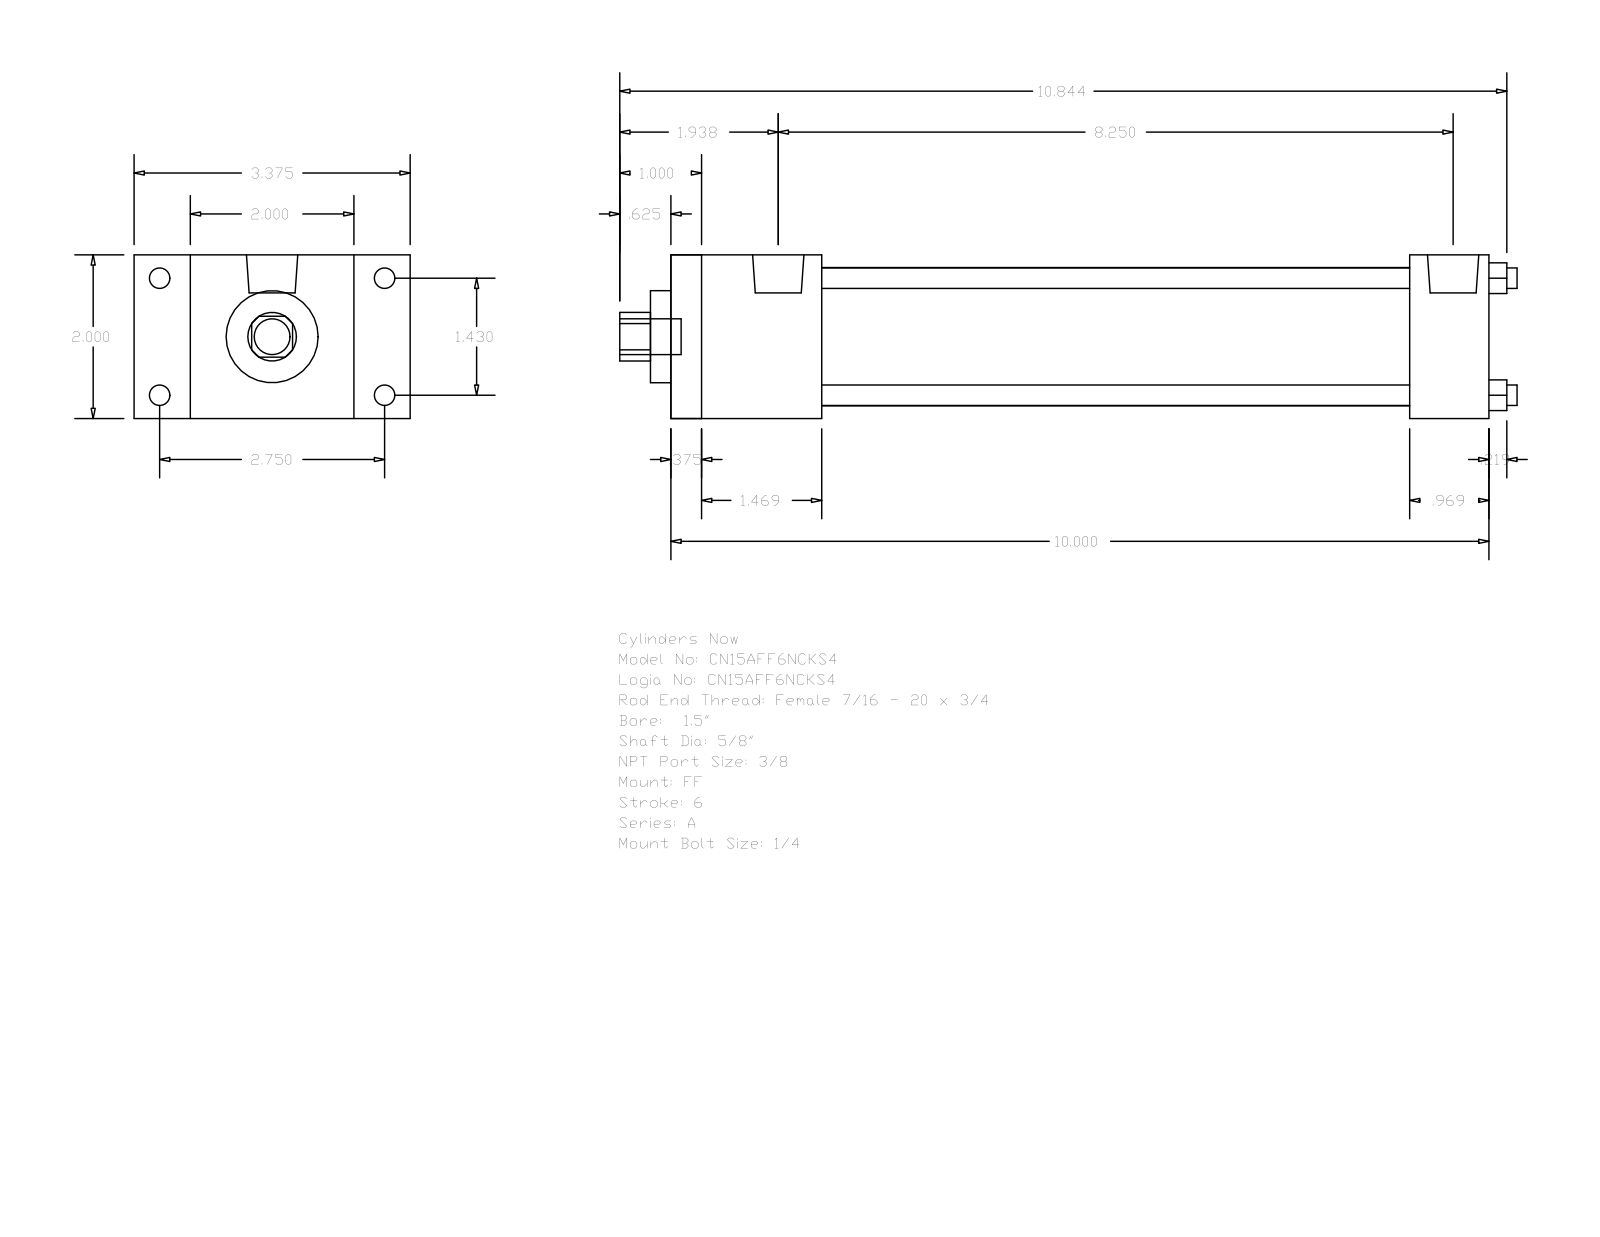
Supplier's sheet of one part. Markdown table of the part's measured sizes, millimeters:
| quantity | value |
| --- | --- |
| part name | A_FF__0150_0.625 |
| STEP written by | GSSL Pune (CONFIG_CONTROL_DESIGN) |
| units | millimeters |
| bodies | 0 solids, 92 faces (64 planar, 28 cylindrical, 0 other) |
| overall size | 278.61 × 85.72 × 50.8 |
| round holes (diameter × count) | 6.35 × 4, 15.88 × 1, 28.57 × 1, 42.93 × 1 |
| round bosses / shafts (diameter × count) | 6.35 × 4, 5.56 × 4, 15.93 × 2, 11.11 × 1 |
| partial cylindrical surfaces (radius × count) | 7.54 × 1 |
| main face-to-face distances | 50.8, 254, 9.52, 244.48, 46.83, 229.39, 37.31, 219.87, 182.56, 207.17 |
| hole center spacings | 25.68, 36.32, 51.36 |
